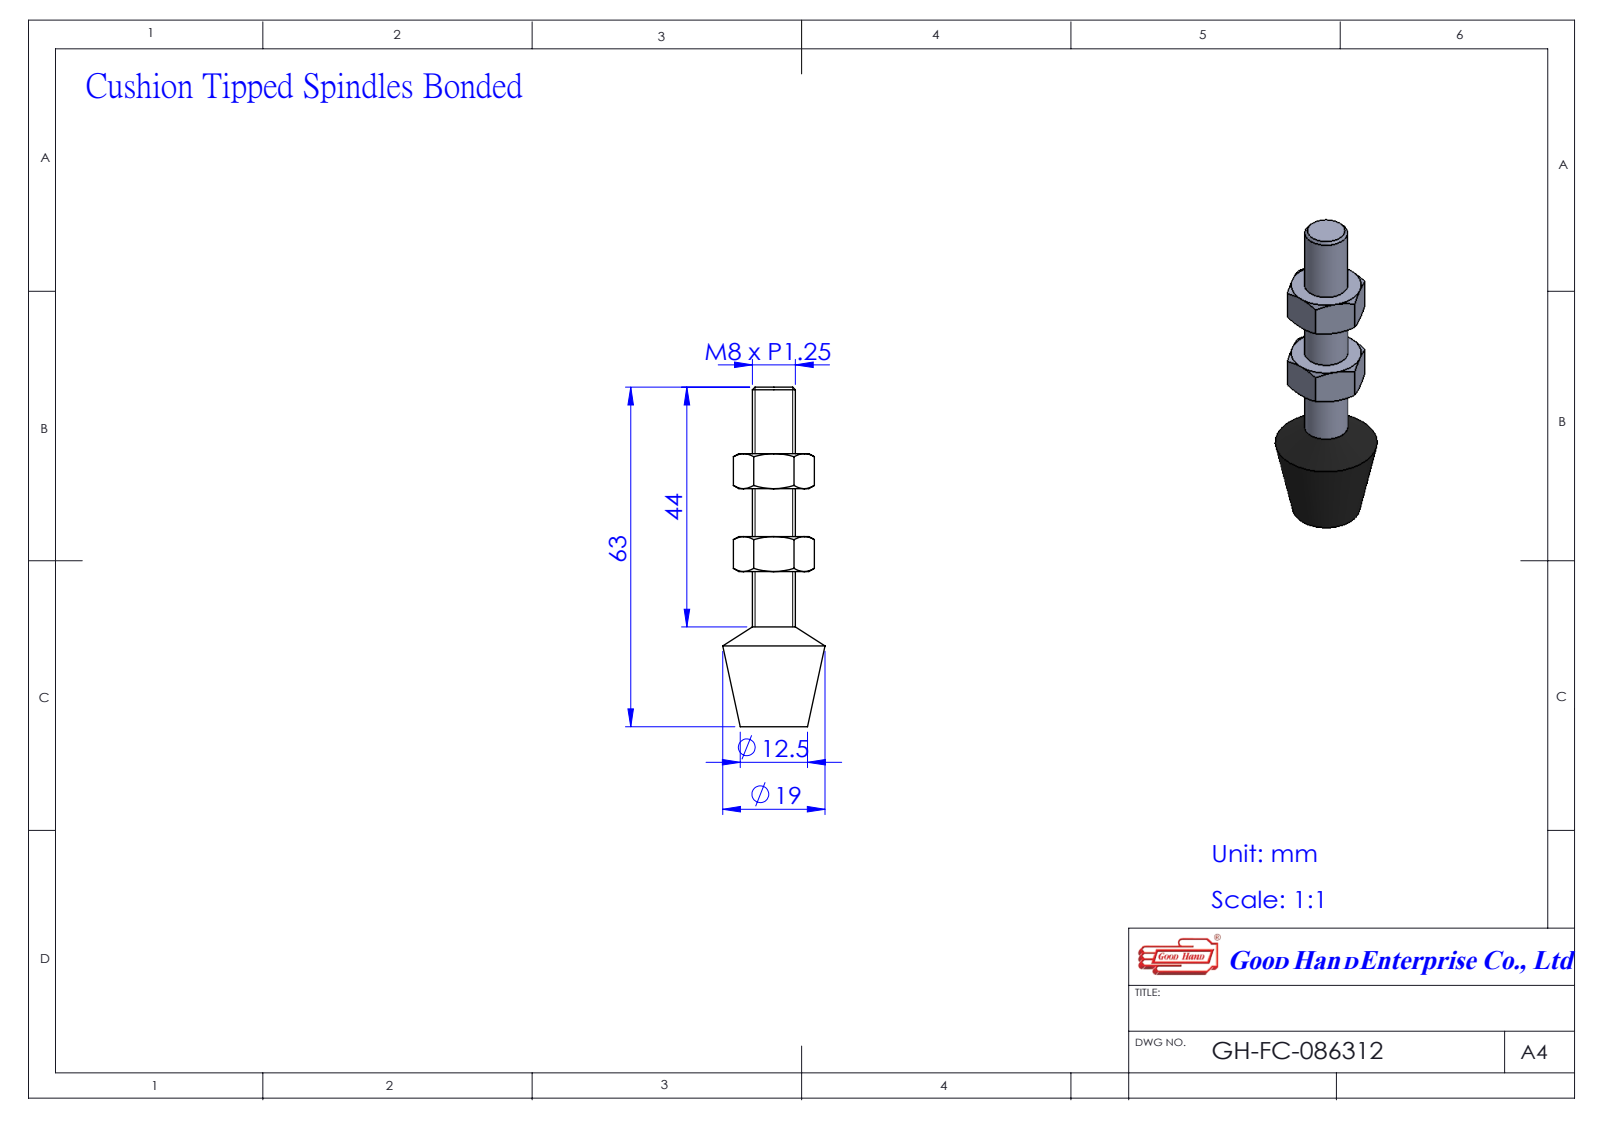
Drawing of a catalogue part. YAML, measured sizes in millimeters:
part_name: "FC-086312; hexagon nut_2_jis_JIS B 1181 Hexagon nut - Class 2 Finished M8 --N; 7408063"
step_written_by: "SolidWorks 2016 (AUTOMOTIVE_DESIGN)"
units: millimeters
bodies: {solids: 3, faces: 66, planar: 18, cylindrical: 10, other: 38}
overall_size: [63, 19, 19]
volume: 7135
surface_area: 3572
round_holes:
  - {diameter: 6.8, count: 1}
  - {diameter: 8, count: 1}
face_to_face_distances: [13, 15.39, 6.5, 35.28, 50.67, 28.78, 44.17, 21.89, 8.89, 63]
